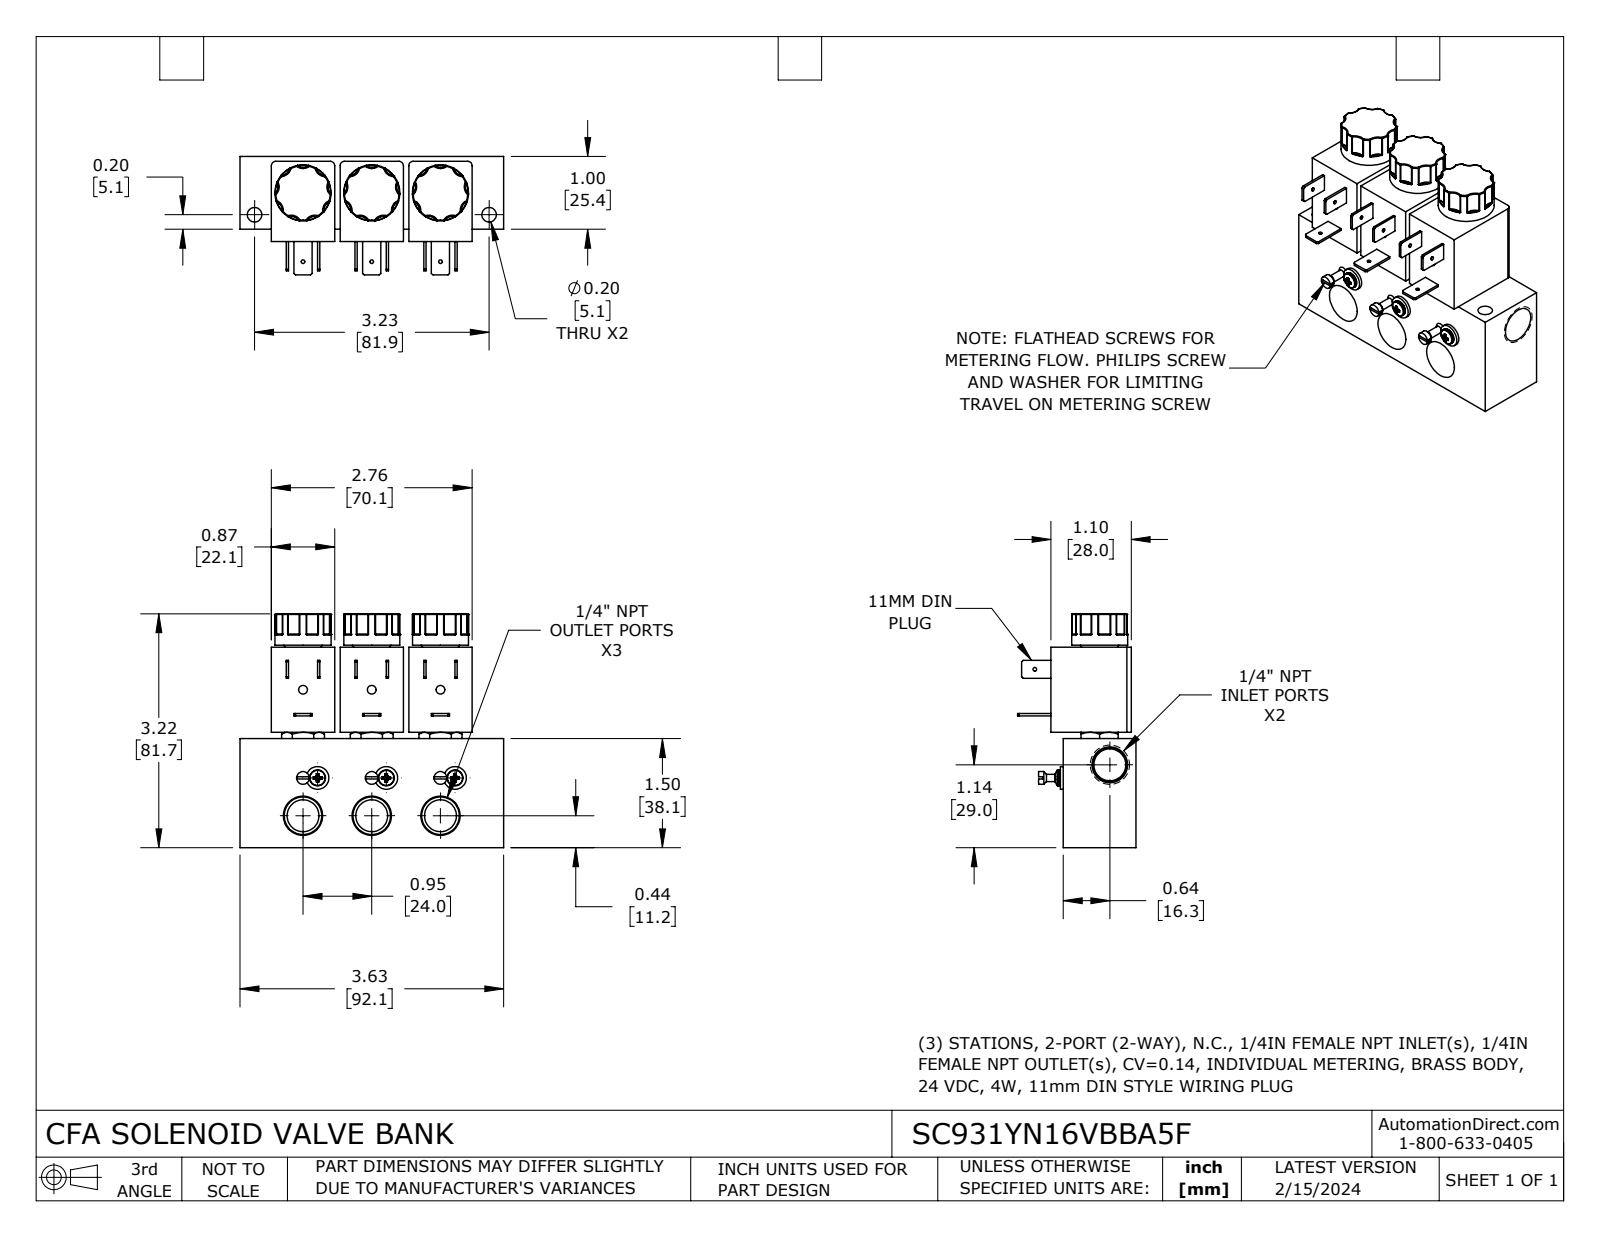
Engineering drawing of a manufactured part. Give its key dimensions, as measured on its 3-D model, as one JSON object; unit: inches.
{"part_name": "SC931YN16VBBA5F", "step_written_by": "SolidWorks 2023 (CONFIG_CONTROL_DESIGN)", "units": "inches", "bodies": {"solids": 1, "faces": 829, "planar": 215, "cylindrical": 197, "other": 417}, "overall_size": [3.625, 3.215, 1.627], "volume_in3": 8.838, "surface_area_in2": 53.67, "round_holes": [[0.05, 4], [0.438, 4], [0.12, 3], [0.2, 2]], "round_bosses_or_shafts": [[0.77, 3], [0.312, 3], [0.219, 3], [0.175, 3], [0.1, 3]], "partial_cylinders_radius": [[0.01, 54], [0.133, 27], [0.06, 6]], "face_to_face_distances": [1, 0.945, 1.169, 0.169, 1.5, 0.945, 1.89, 0.065, 0.935, 1.104], "hole_center_spacings": [0.945, 0.945, 1.732, 1.89, 1.973, 1.973, 2.564, 0.928]}
